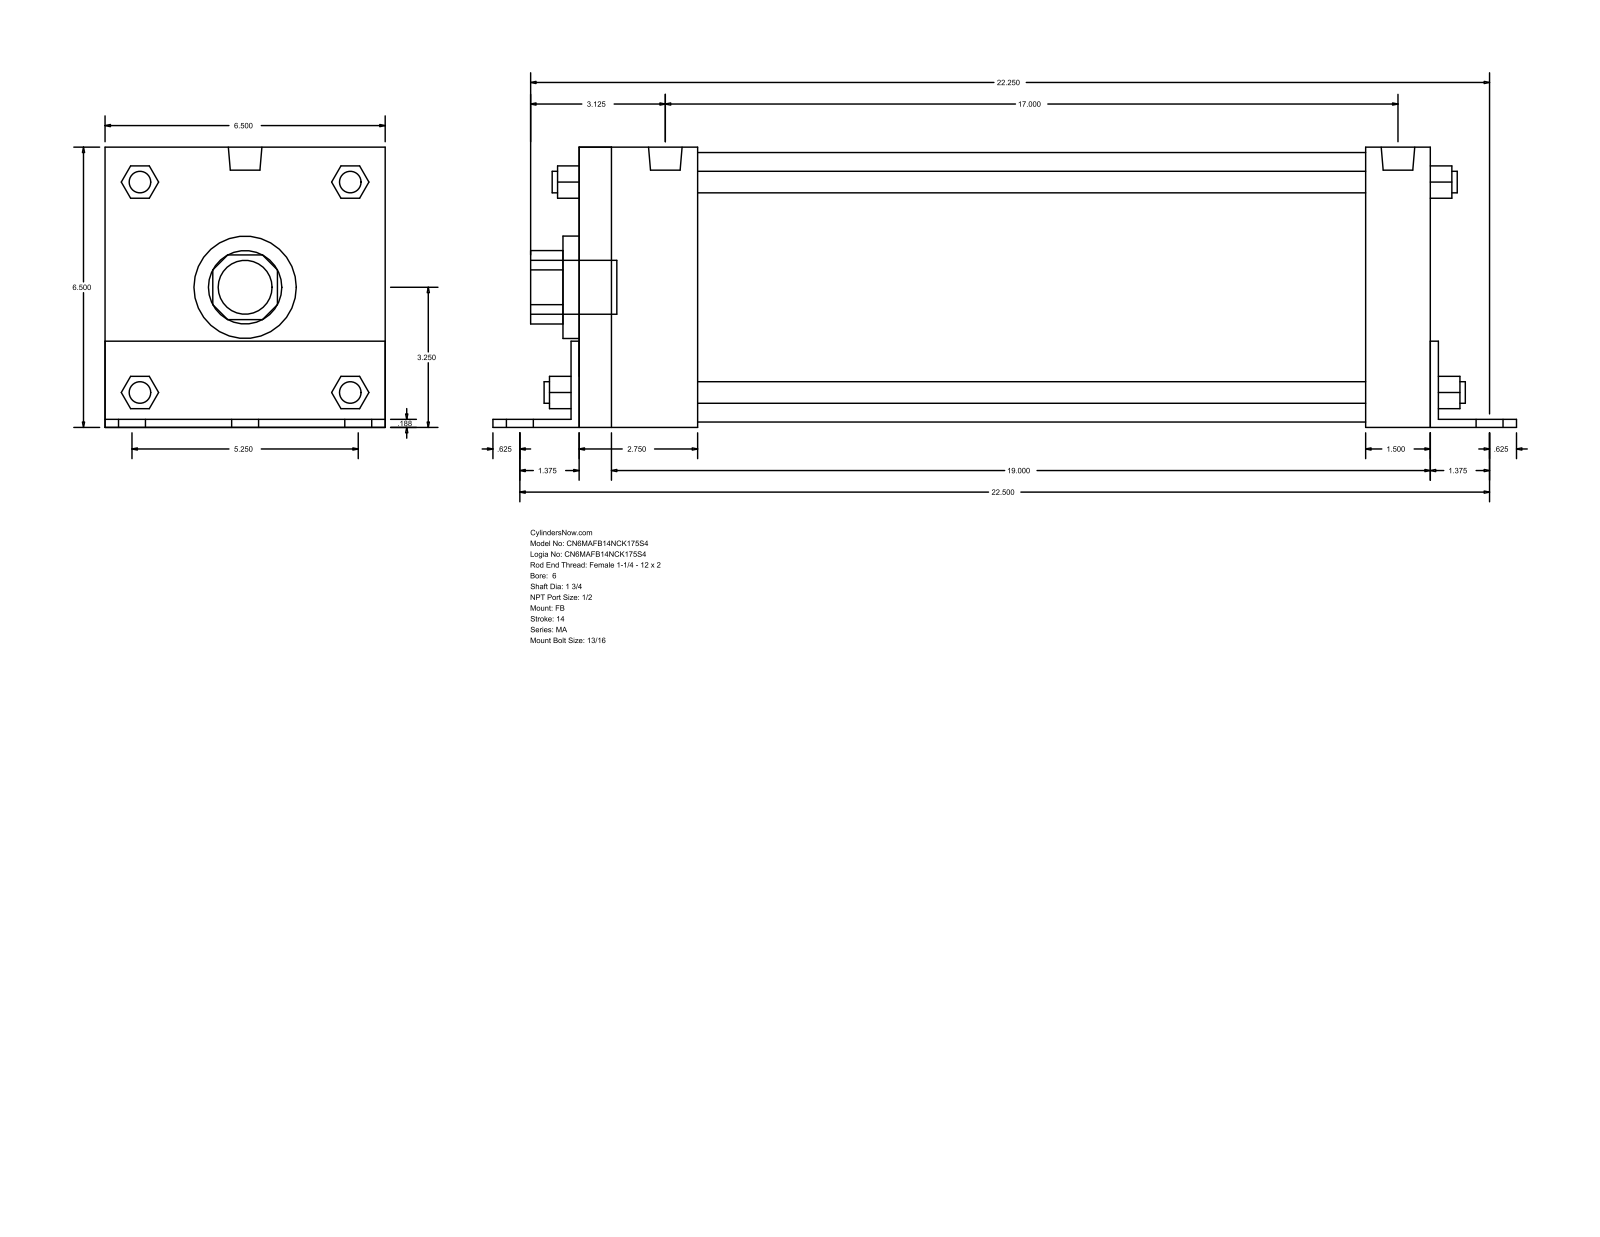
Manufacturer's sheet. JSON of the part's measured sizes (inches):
{"part_name": "MA_FB__0600_1.75", "step_written_by": "GSSL Pune (CONFIG_CONTROL_DESIGN)", "units": "inches", "bodies": {"solids": 0, "faces": 140, "planar": 105, "cylindrical": 35, "other": 0}, "overall_size": [23.75, 6.502, 6.5], "round_holes": [[1.75, 1], [2.375, 1], [6.25, 1]], "round_bosses_or_shafts": [[0.813, 6], [0.687, 4], [0.5, 4], [0.778, 2], [1.25, 1]], "partial_cylinders_radius": [[0.852, 1], [1.262, 1]], "face_to_face_distances": [6.5, 0.187, 19.75, 6.502, 19.938, 0.185, 6.315, 20.125, 1.5, 2.937]}
